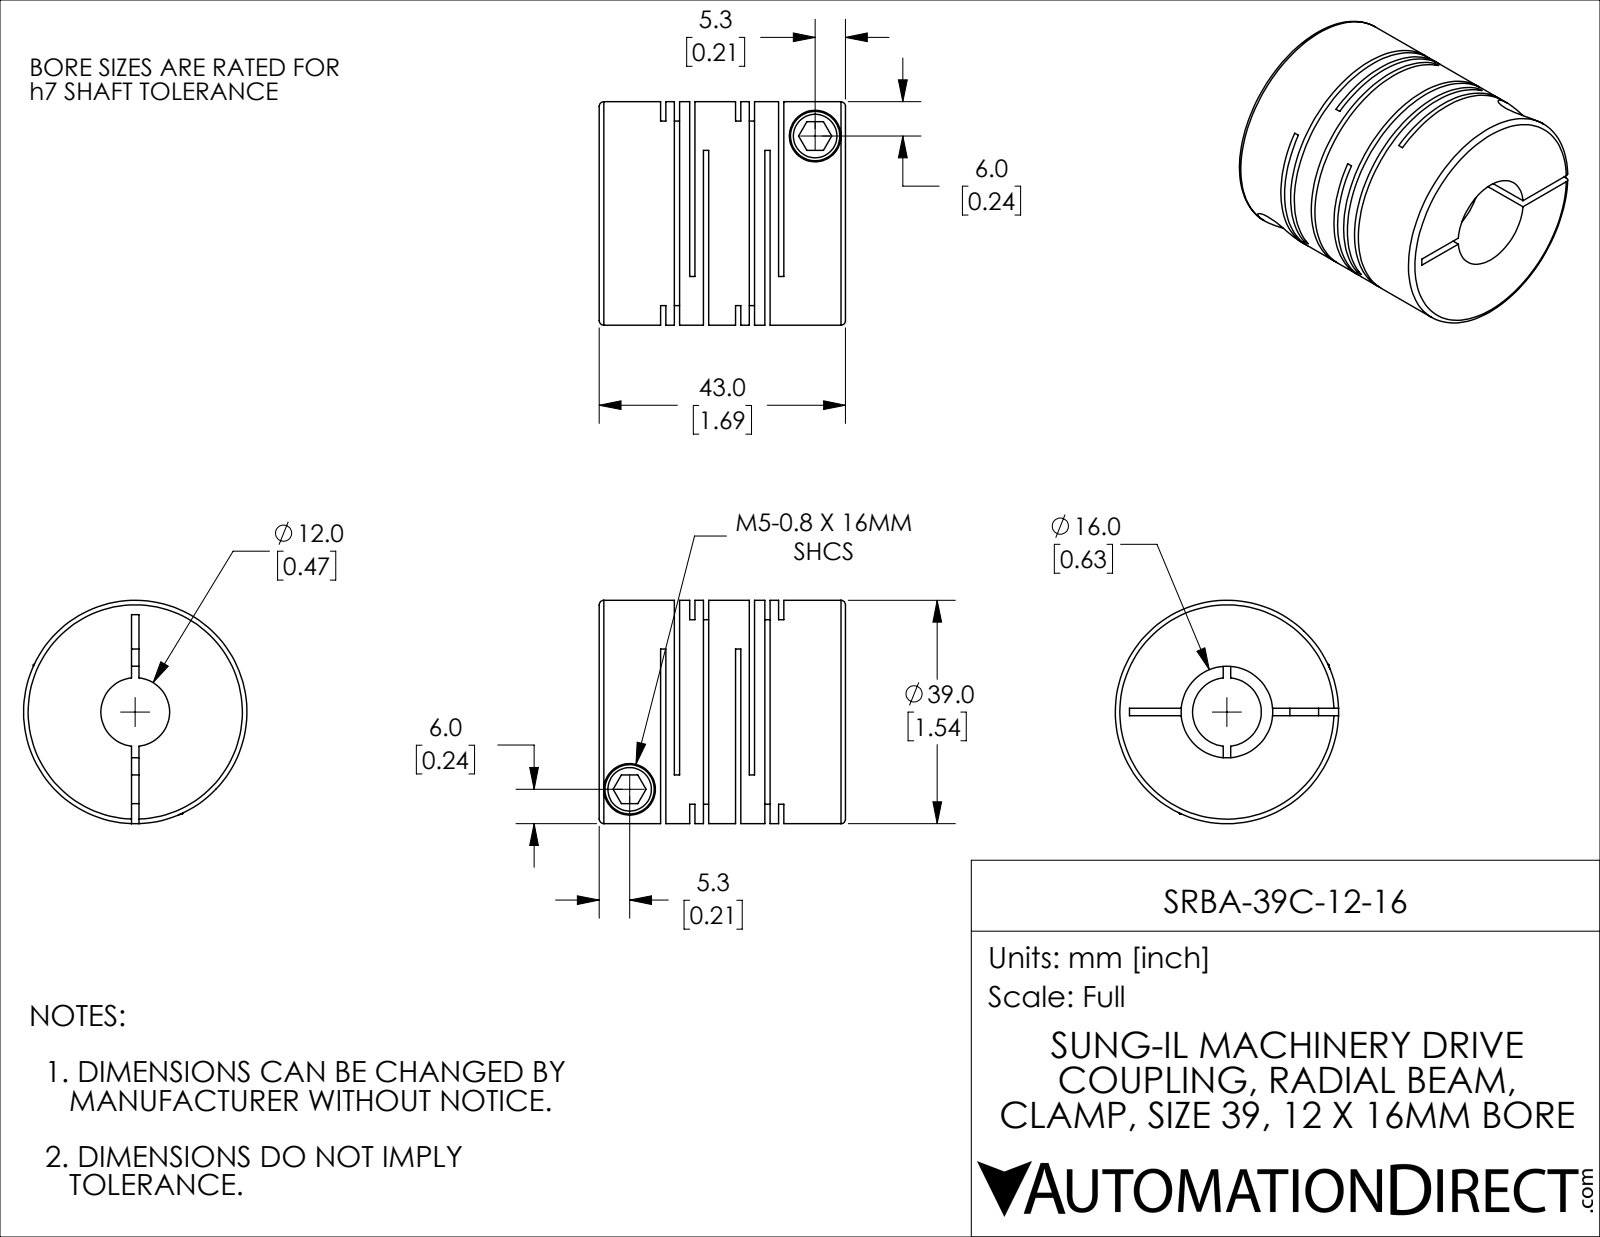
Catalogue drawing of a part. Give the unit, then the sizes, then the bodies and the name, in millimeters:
Units: millimetres
Overall size (bounding box): 43 × 39 × 39
Round holes (diameter × count): ⌀5 ×2, ⌀9 ×2, ⌀12 ×1, ⌀16 ×1
Round bosses / shafts (diameter × count): ⌀8.6 ×2, ⌀39 ×1
Main face-to-face distances: 13.1, 0.92, 2.4, 5.1, 10.7, 14.02, 18.2, 3.32, 15.5, 1.48
Volume: 36 229 mm³ · Surface area: 23 061 mm²
Bodies: 1 solid, 114 faces (60 planar, 42 cylindrical, 12 other)
Part name (STEP PRODUCT): SRBA-39C-12-16
STEP written by: SolidWorks 2021 (CONFIG_CONTROL_DESIGN)
